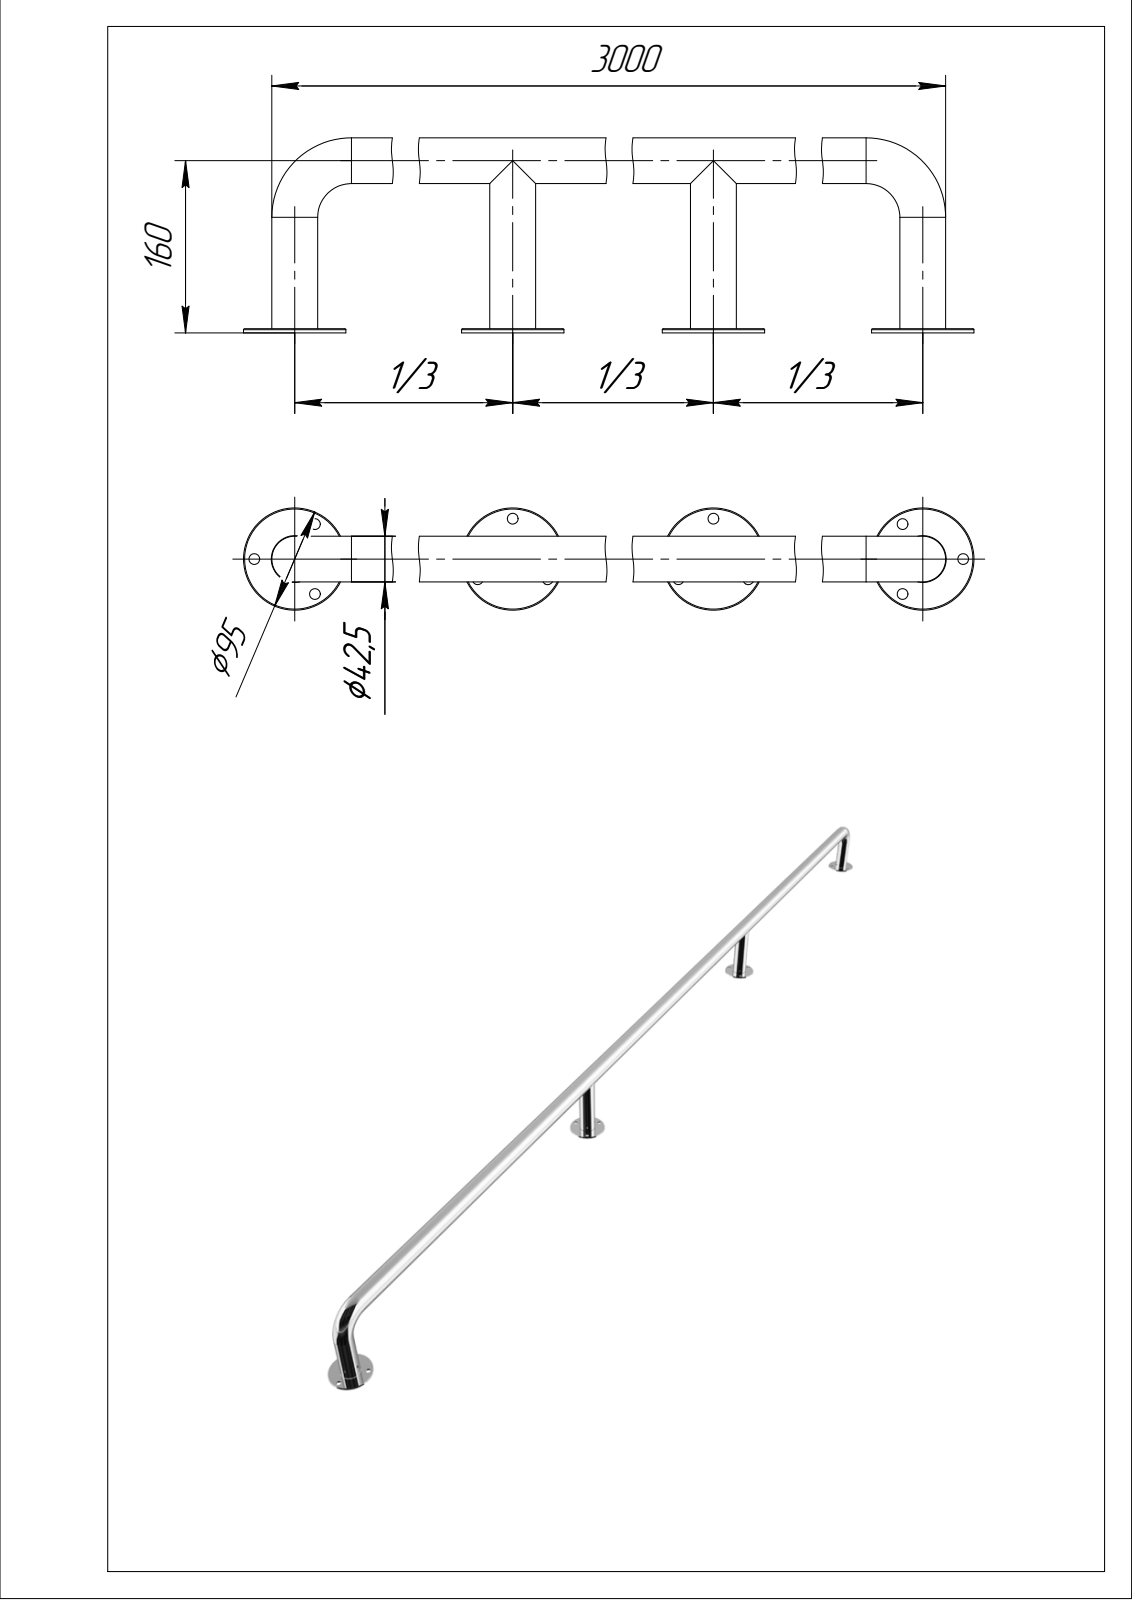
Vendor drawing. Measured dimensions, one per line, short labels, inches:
name: Сборка; Деталь; Фланец; Тр 2-42.5
written by: ASCON Math Kernel (AUTOMOTIVE_DESIGN)
unit: in
bodies: 11 solids, 72 faces (20 planar, 38 cylindrical, 14 other)
size: 120.177 × 7.136 × 3.74
volume: 36.71 in³; area: 1 529 in²
holes: 12× ⌀0.394, 3× ⌀1.594, 2× ⌀0.236, 2× ⌀1.555, 2× ⌀1.713, 1× ⌀1.673
bosses: 4× ⌀3.74, 4× ⌀1.673, 2× ⌀1.535
face distances: 0.157, 0.472, 0.315, 6.693, 6.535, 6.22
hole spacings: 1.476, 2.557, 2.557, 38.096, 38.813, 76.897, 115.706, 117.182
